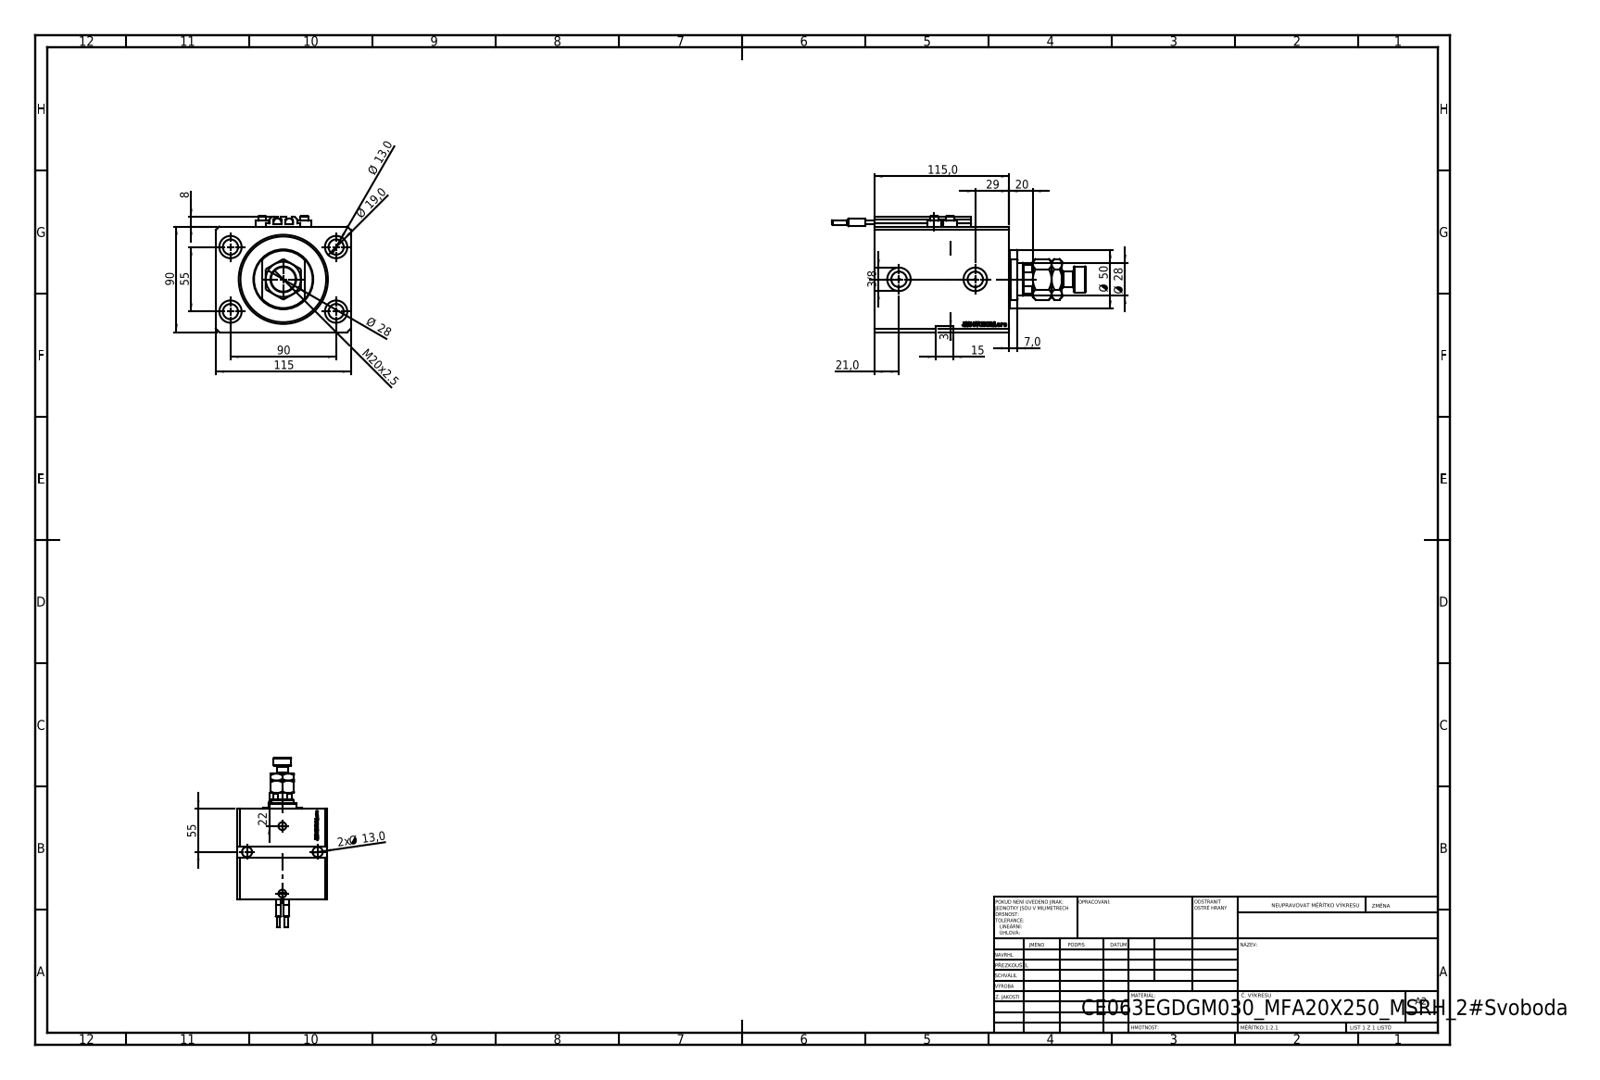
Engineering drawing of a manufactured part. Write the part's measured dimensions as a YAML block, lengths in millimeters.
part_name: "SWITCH_V250CE; V250CE_E_Body; MFA; ALLEN BOLT V250CE (+2 more)"
step_written_by: "SolidWorks 2019 (CONFIG_CONTROL_DESIGN)"
units: millimeters
bodies: {solids: 11, faces: 1227, planar: 595, cylindrical: 154, other: 478}
overall_size: [216, 115, 99]
volume: 1053000
surface_area: 173003
round_holes:
  - {diameter: 13, count: 6}
  - {diameter: 1.25, count: 4}
  - {diameter: 4, count: 4}
  - {diameter: 19, count: 4}
  - {diameter: 10, count: 2}
  - {diameter: 13.16, count: 2}
  - {diameter: 20, count: 2}
  - {diameter: 18.5, count: 1}
  - {diameter: 28, count: 1}
  - {diameter: 63, count: 1}
  - {diameter: 76, count: 1}
round_bosses_or_shafts:
  - {diameter: 11.6, count: 4}
  - {diameter: 7, count: 4}
  - {diameter: 6.8, count: 2}
  - {diameter: 6.5, count: 2}
  - {diameter: 4, count: 2}
  - {diameter: 50, count: 1}
  - {diameter: 22, count: 1}
  - {diameter: 14, count: 1}
partial_cylinders:
  - {radius: 0.2, count: 10}
  - {radius: 13.5, count: 1}
face_to_face_distances: [115, 90, 20, 95, 97.1, 17.9, 77.1, 30, 65, 13]
hole_center_spacings: [52.74, 90, 13.6, 27.39, 28.46, 33.62, 36, 38.48]
